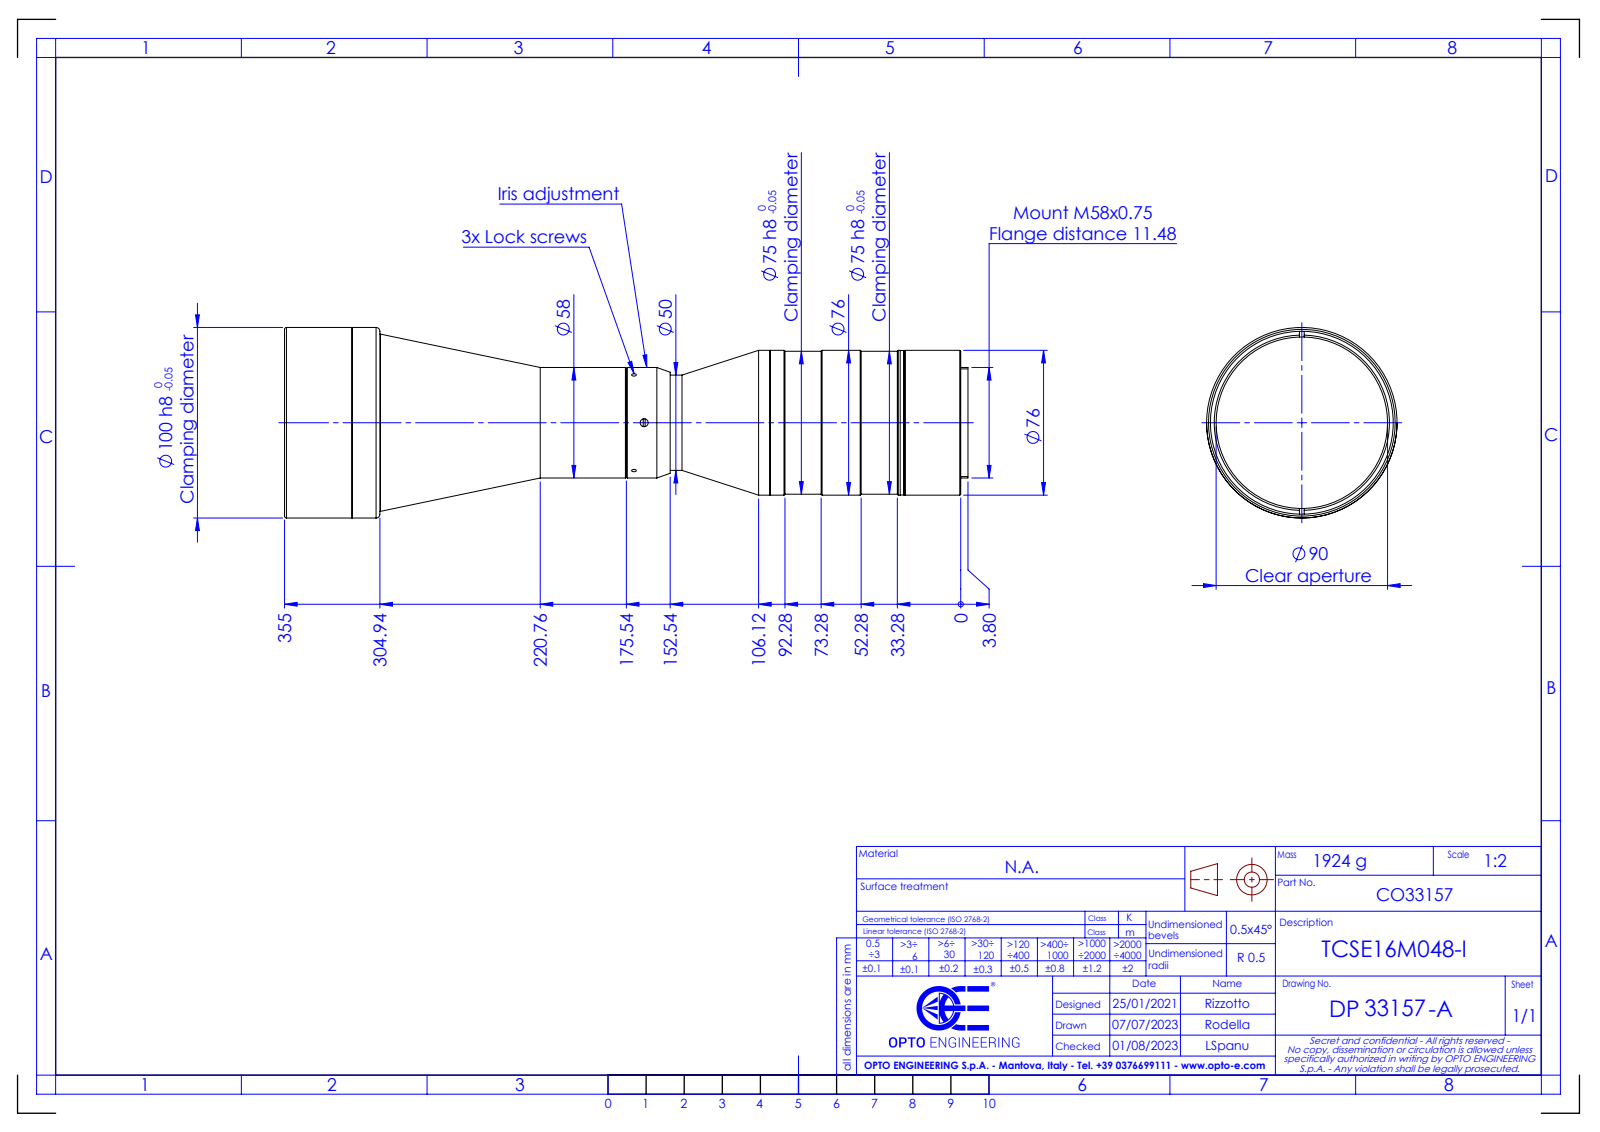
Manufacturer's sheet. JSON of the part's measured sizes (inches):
{"part_name": "DP33157-A_TCSE16M048-I", "step_written_by": "SolidWorks 2021 (CONFIG_CONTROL_DESIGN)", "units": "inches", "bodies": {"solids": 0, "faces": 108, "planar": 24, "cylindrical": 50, "other": 34}, "overall_size": [14.126, 3.937, 3.937], "round_holes": [[0.098, 3], [0.165, 1], [2.126, 1], [2.52, 1], [2.717, 1], [3.543, 1], [3.78, 1]], "round_bosses_or_shafts": [[3.937, 1], [3.661, 1], [2.992, 1], [2.984, 1], [2.953, 1], [2.283, 1], [1.969, 1]], "face_to_face_distances": [12.581, 5.67, 6.911, 1.375, 7.045, 13.956, 13.579, 12.204, 6.534, 0.377], "hole_center_spacings": [0.211]}
